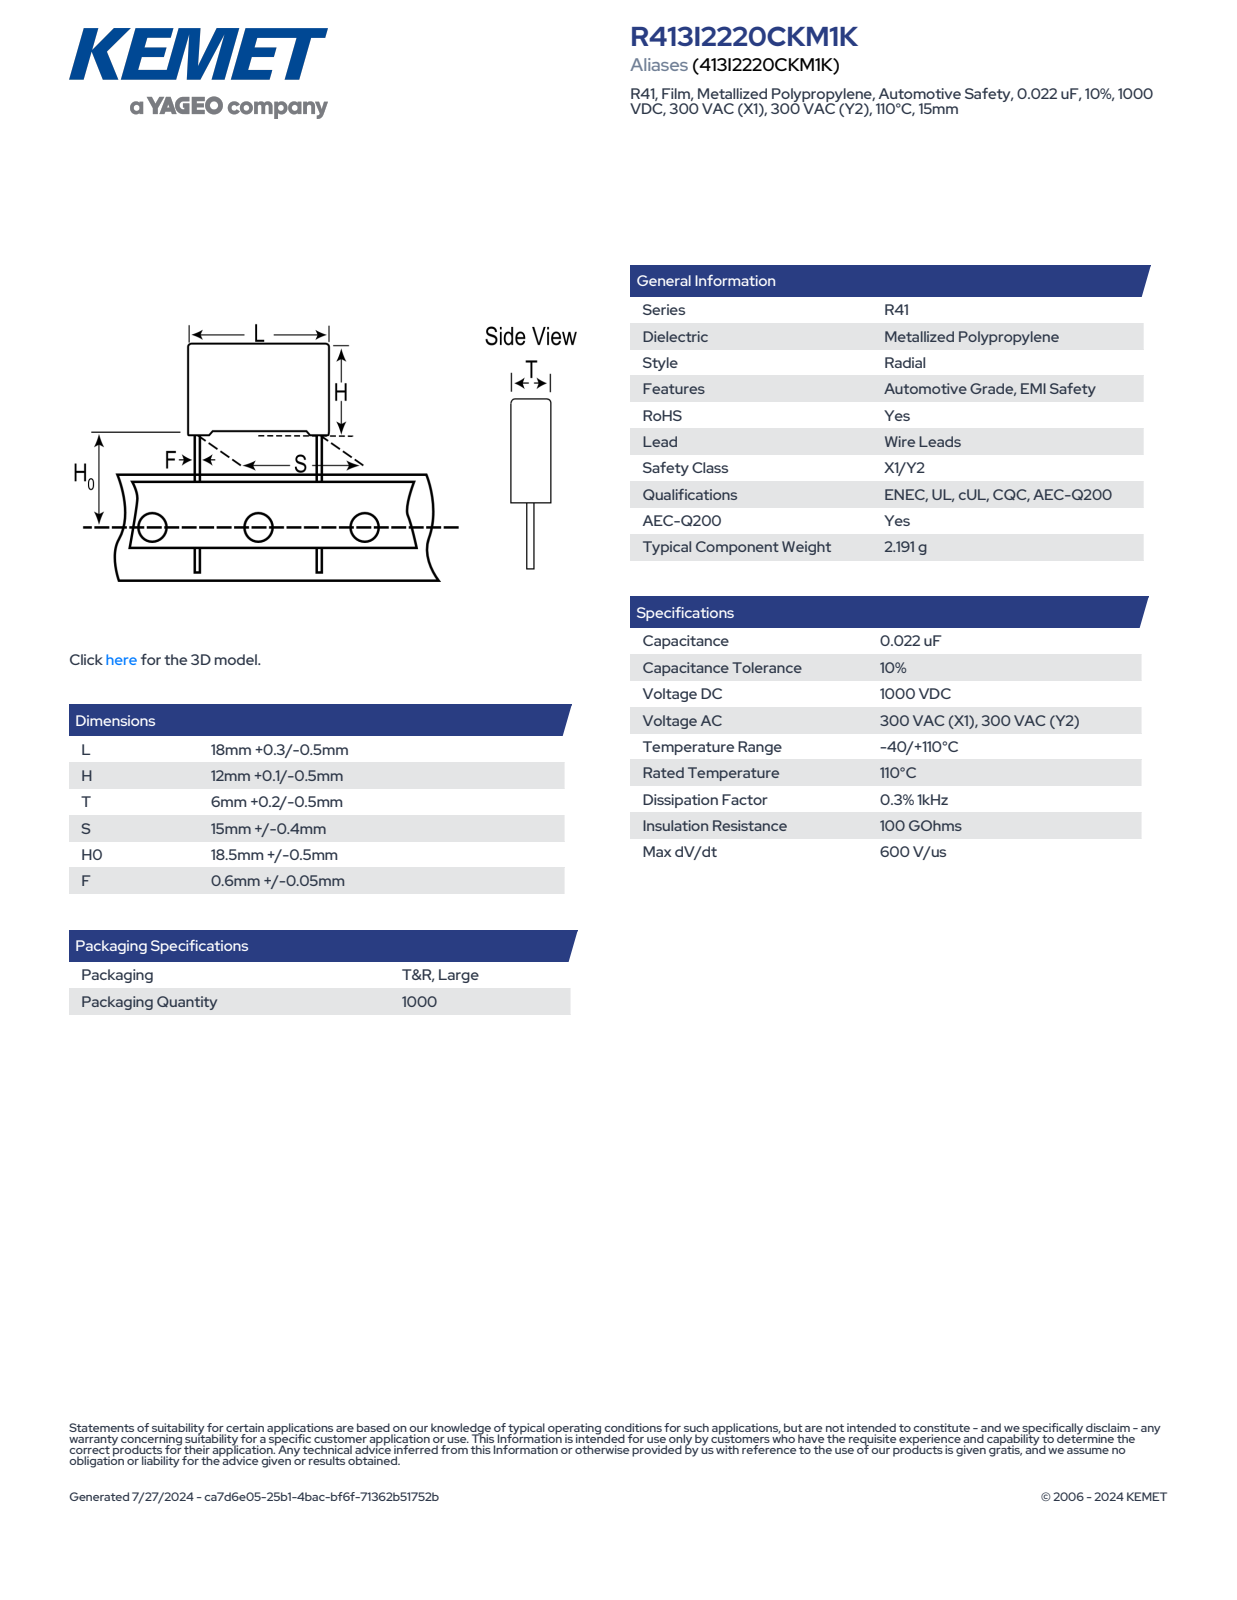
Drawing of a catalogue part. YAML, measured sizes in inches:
part_name: "CFR_RB2_18X12X6_L18.3H12.1T6.2S15H019F0.65"
step_written_by: "SolidWorks 2020 (AUTOMOTIVE_DESIGN)"
units: inches
bodies: {solids: 4, faces: 85, planar: 77, cylindrical: 8, other: 0}
overall_size: [1.224, 0.72, 0.244]
volume: 0.08
surface_area: 1.44
round_bosses_or_shafts:
  - {diameter: 0.026, count: 2}
partial_cylinders:
  - {radius: 0.02, count: 4}
face_to_face_distances: [0.244, 0.447, 0.72, 0.024, 0.22, 0.03, 0.476, 0.017, 0.013, 0.46]
